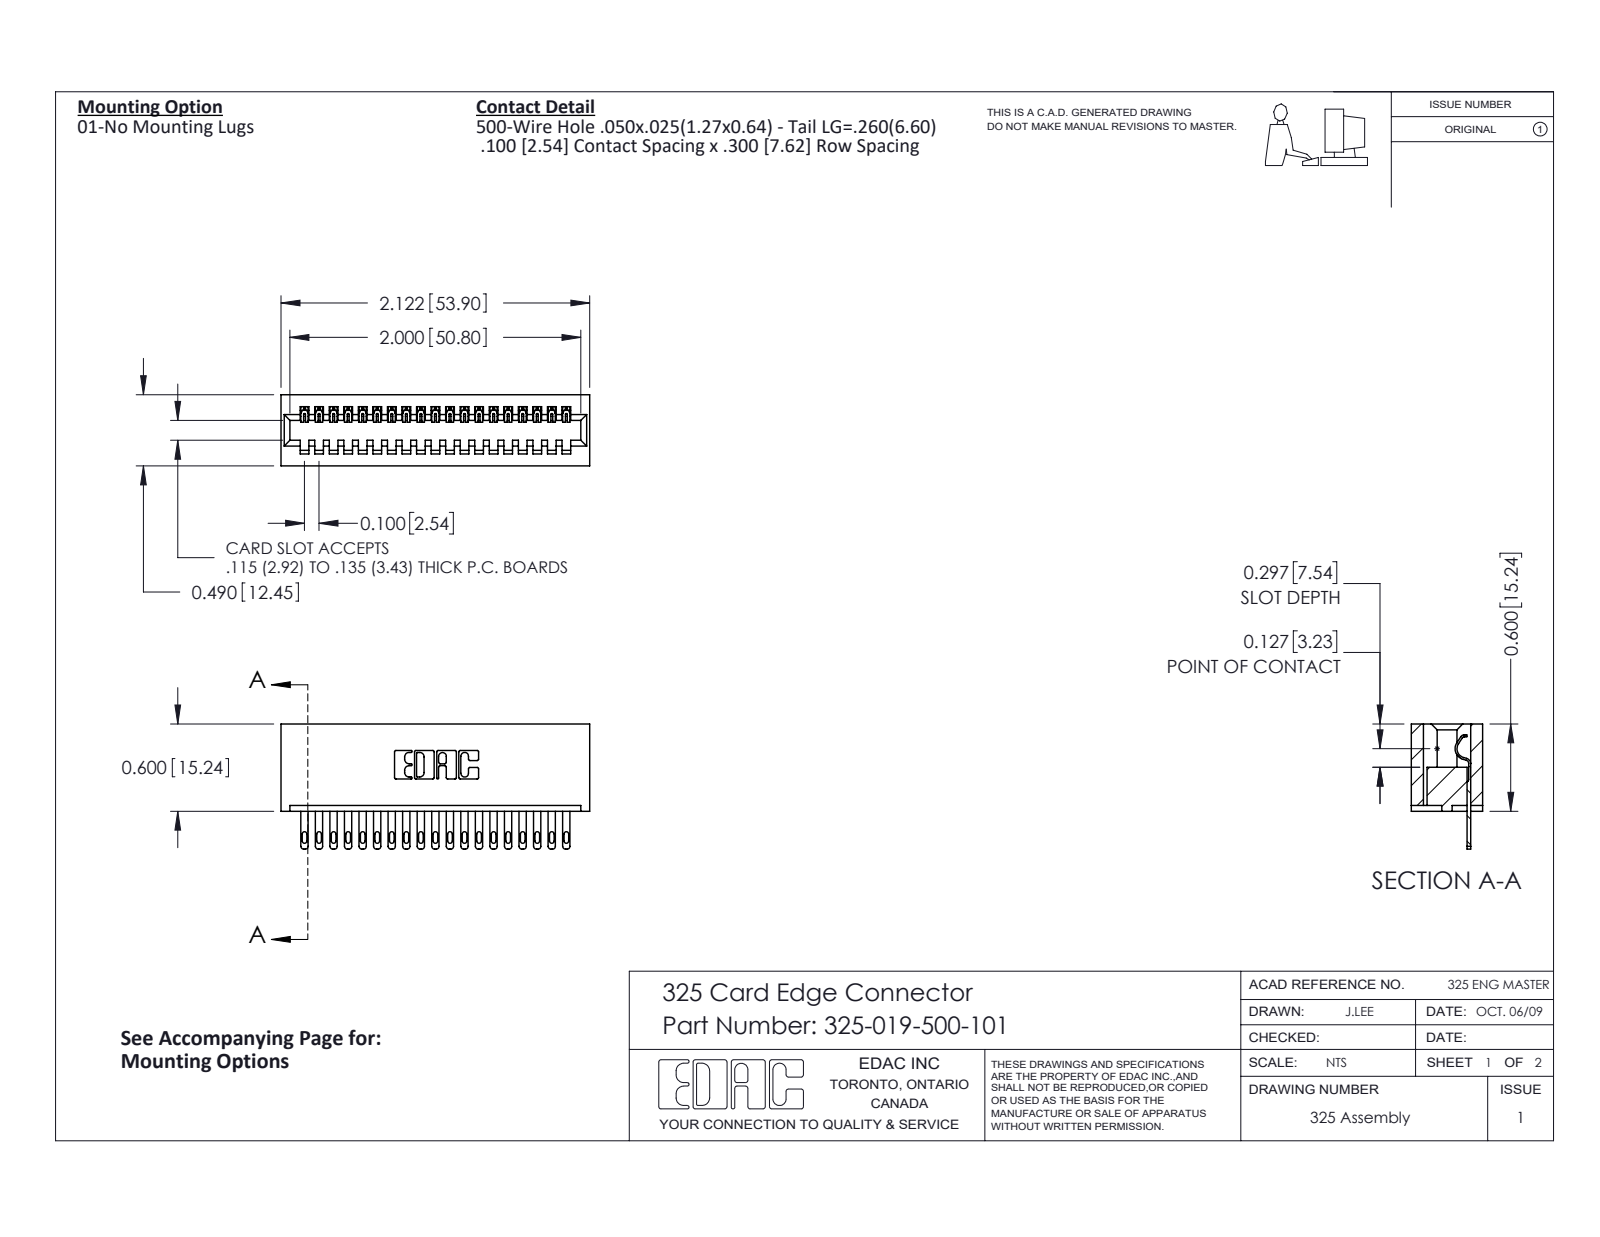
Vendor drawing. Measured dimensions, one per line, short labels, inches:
name: 325 Part_Lugless; 325-019-500-101; 325-292-001_325-293-100
written by: SolidWorks 2016 (CONFIG_CONTROL_DESIGN)
unit: in
bodies: 20 solids, 1132 faces (750 planar, 382 cylindrical, 0 other)
size: 2.122 × 0.86 × 0.49
volume: 0.442 in³; area: 12.49 in²
rounds: 38× R0.006, 38× R0.016, 38× R0.02, 22× R0.01, 6× R0.007, 6× R0.031, 3× R0.026, 1× R0.014
face distances: 0.083, 0.407, 0.3, 0.49, 0.107, 0.383, 0.025, 0.1, 0.2, 0.56
